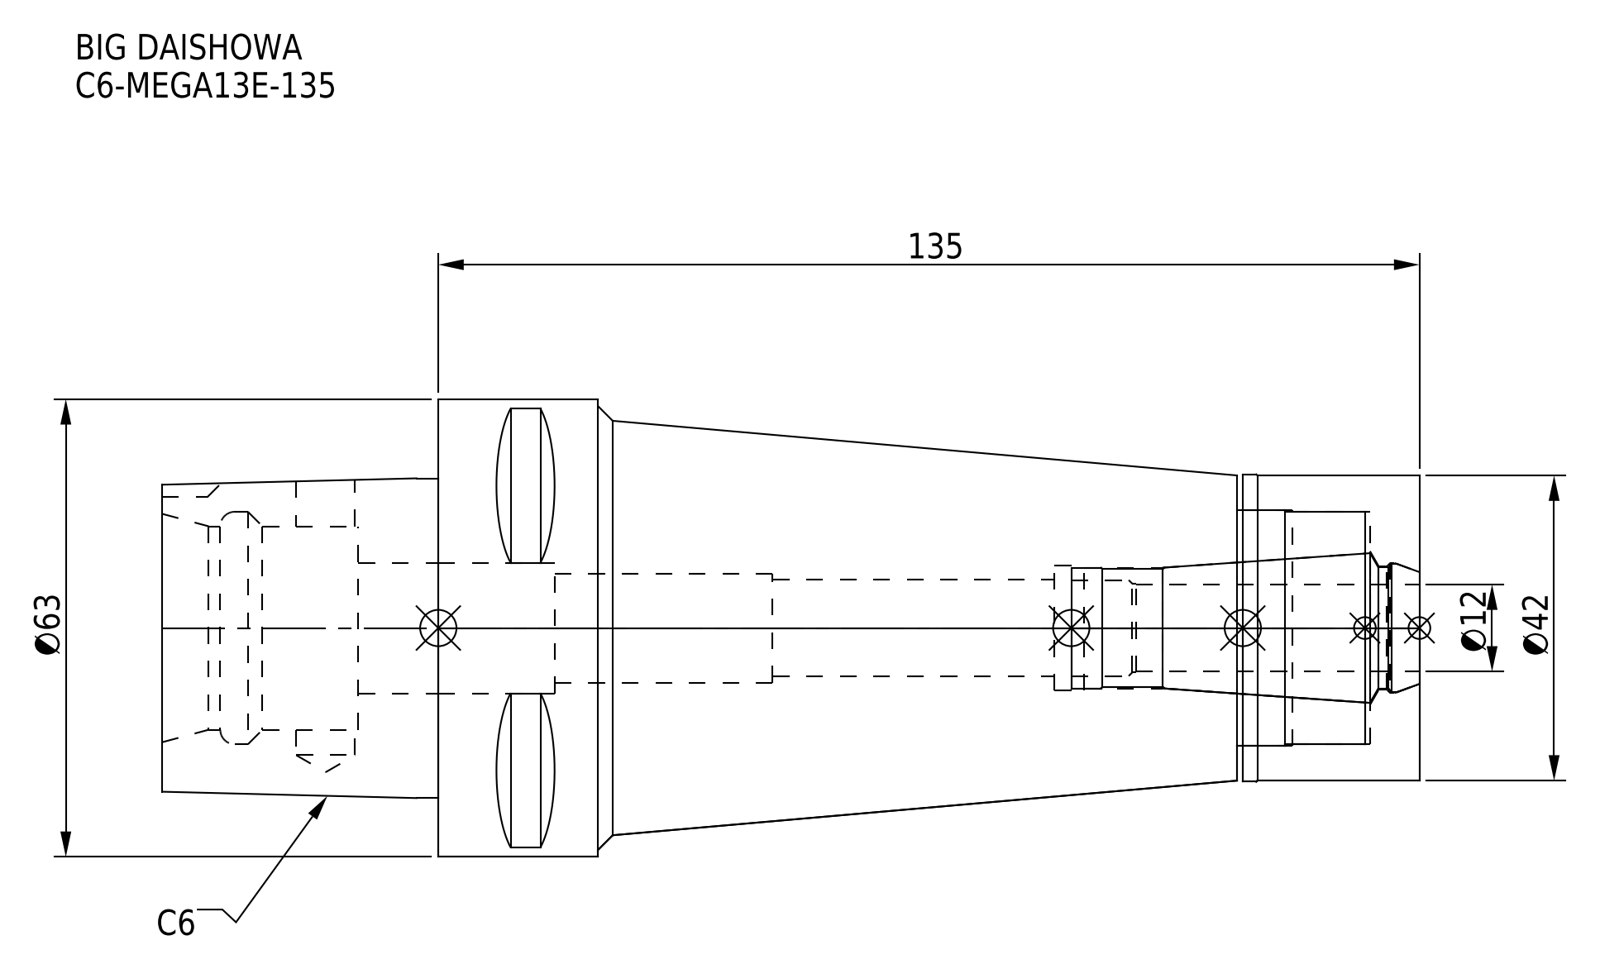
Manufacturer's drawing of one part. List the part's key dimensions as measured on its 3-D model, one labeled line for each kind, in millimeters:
Part name (STEP PRODUCT): C6-MEGA13E-135-120_ASM.stp; MEN13_1.stp; C6-MEGA13E-135; C6-MEGA13E-135_1.stp (+3 more)
STEP written by: SolidWorks 2019 (CONFIG_CONTROL_DESIGN)
Units: millimetres
Bodies: 2 solids, 100 faces (37 planar, 39 cylindrical, 24 other)
Overall size (bounding box): 173 × 63 × 63
Volume: 279 391 mm³ · Surface area: 47 106 mm²
Round holes (diameter × count): ⌀8.1 ×1, ⌀13.3 ×1, ⌀15 ×1, ⌀16.6 ×1, ⌀17 ×1, ⌀17.2 ×1, ⌀17.9 ×1, ⌀18 ×1, ⌀28 ×1, ⌀32 ×1, ⌀32.5 ×1
Round bosses / shafts (diameter × count): ⌀63 ×1, ⌀42.3 ×1, ⌀42 ×1
Partial cylindrical surfaces — rounded edges, fillets, slot ends (radius × count): R5 ×1
Main face-to-face distances: 135, 25.1, 24.3, 110.7, 0.8, 109.9, 127.5, 173, 148.7, 147.9
